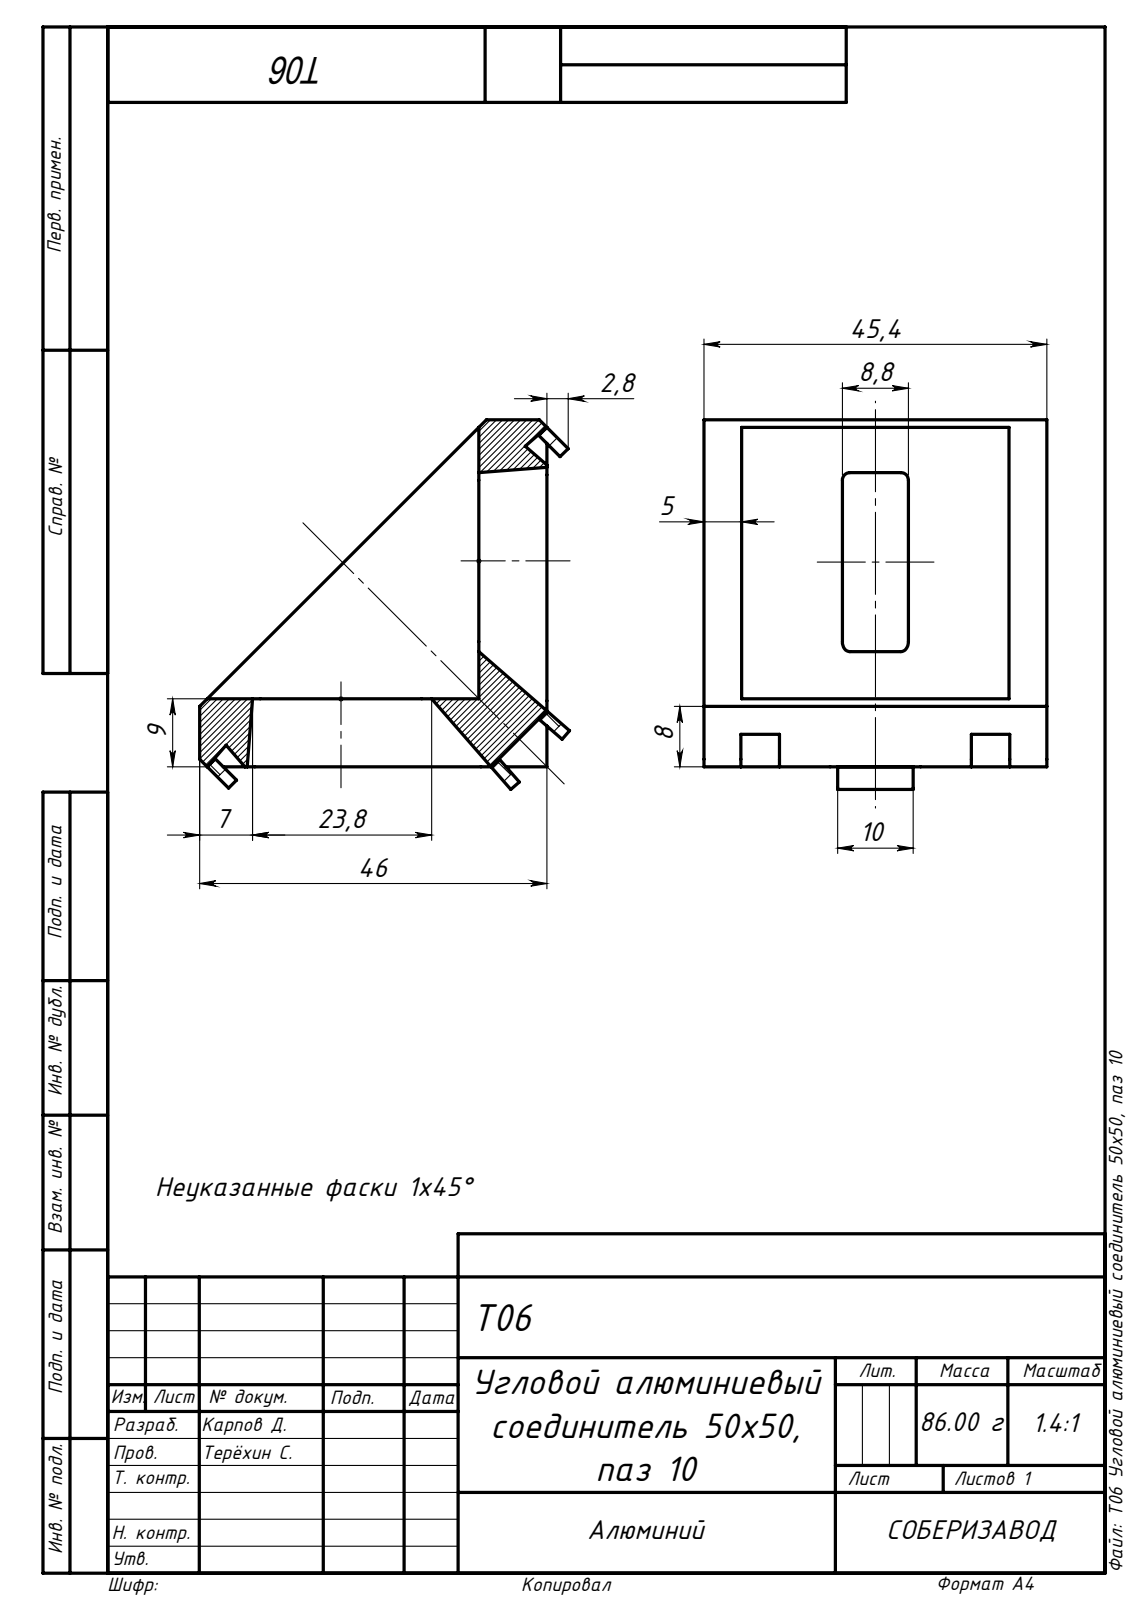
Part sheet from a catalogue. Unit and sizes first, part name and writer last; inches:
Units: inches
Overall size (bounding box): 1.93 × 1.93 × 1.788
Partial cylindrical surfaces — rounded edges, fillets, slot ends (radius × count): R0.039 ×8
Main face-to-face distances: 0.197, 0.354, 1.788, 1.591, 0.157, 0.722, 1.066, 0.525, 0.869, 1.394
Volume: 1.901 in³ · Surface area: 22.04 in²
Bodies: 5 solids, 100 faces (92 planar, 8 cylindrical, 0 other)
Part name (STEP PRODUCT): T06 Угловой алюминиевый соединитель 50x50, паз 10
STEP written by: SolidWorks 2021 (AUTOMOTIVE_DESIGN)
